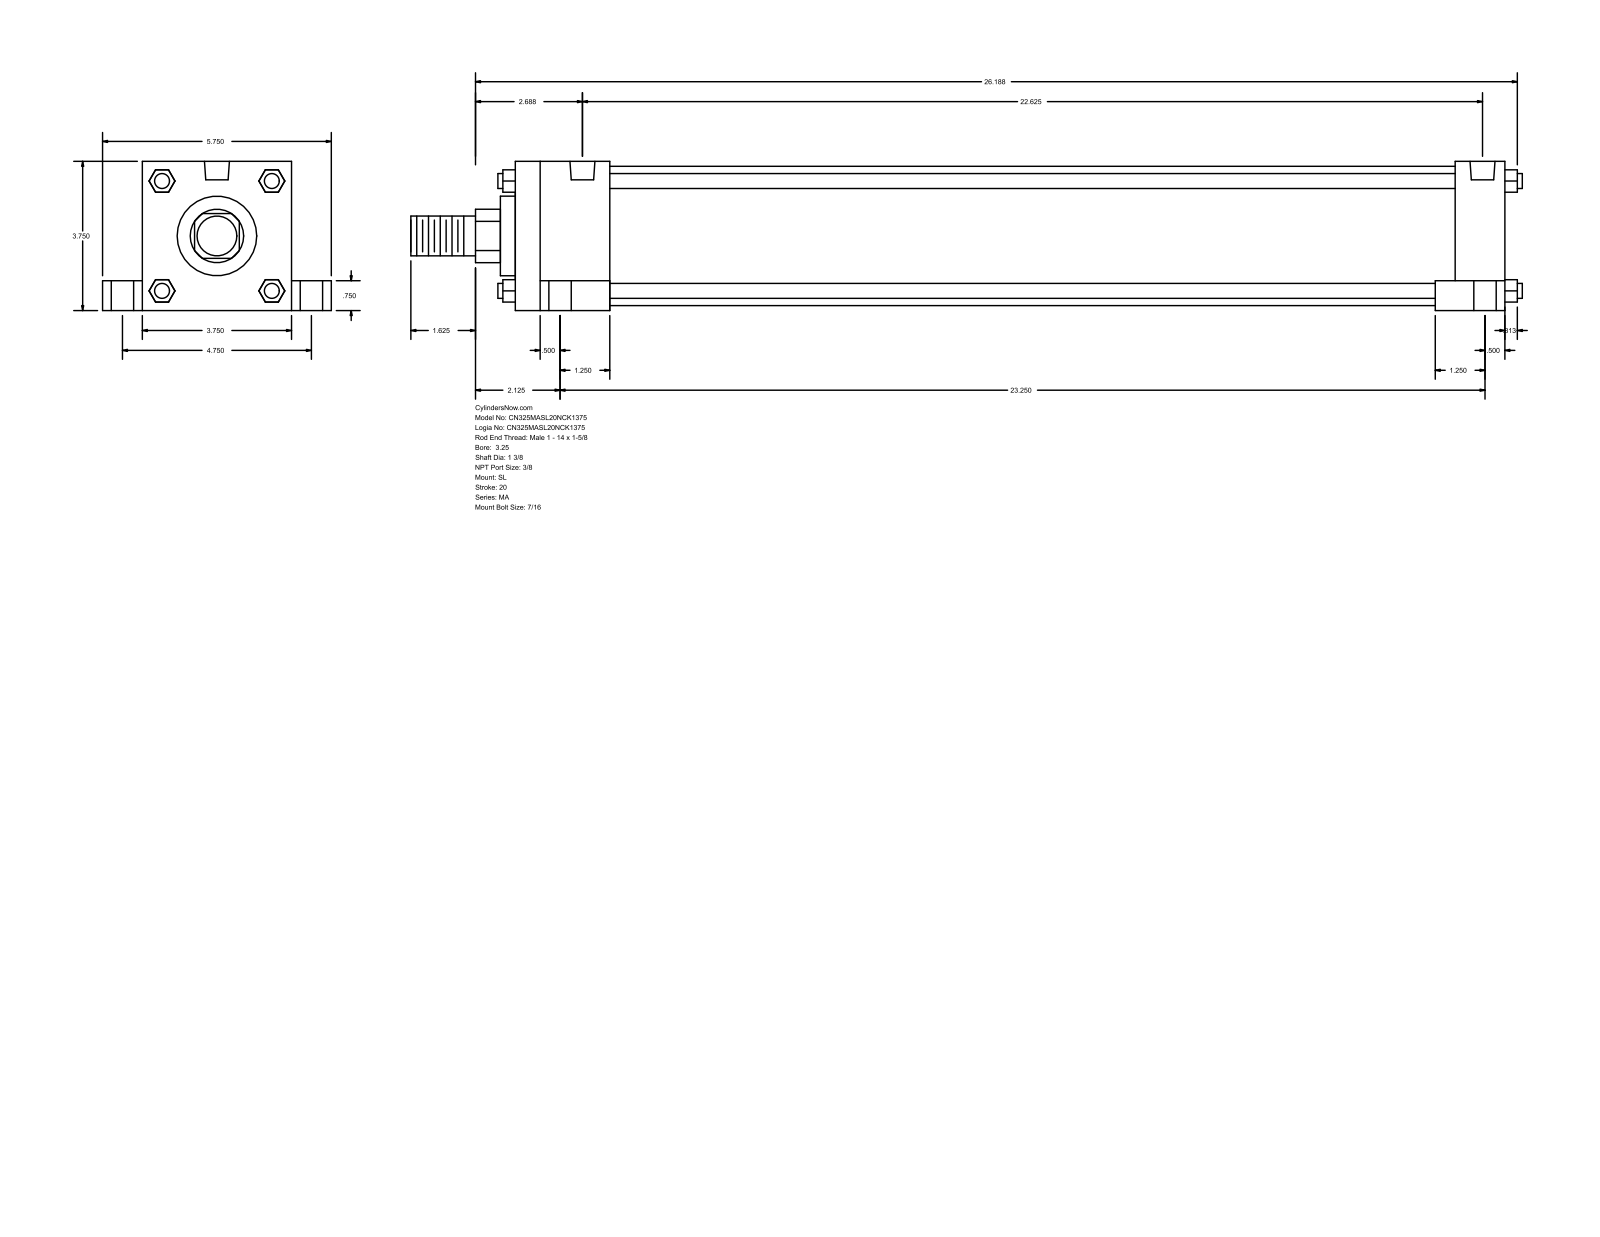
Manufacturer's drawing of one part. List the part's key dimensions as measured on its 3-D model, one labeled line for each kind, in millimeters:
Part name (STEP PRODUCT): MA_SL__0325_1.375
STEP written by: GSSL Pune (CONFIG_CONTROL_DESIGN)
Units: millimetres
Bodies: 0 solids, 148 faces (112 planar, 36 cylindrical, 0 other)
Overall size (bounding box): 709.61 × 146.05 × 95.25
Round holes (diameter × count): ⌀11.11 ×4, ⌀14.29 ×4, ⌀20.64 ×4, ⌀15.93 ×2
Round bosses / shafts (diameter × count): ⌀9.53 ×4, ⌀88.9 ×1, ⌀50.8 ×1, ⌀34.92 ×1, ⌀25.4 ×1
Partial cylindrical surfaces — rounded edges, fillets, slot ends (radius × count): R17.06 ×1
Main face-to-face distances: 95.24, 631.83, 25.41, 120.65, 600.08, 31.75, 60.32, 539.76, 571.51, 19.05
Hole centre spacings: 4.77, 60.35, 60.66, 62, 63.27, 120.66, 565.14, 569.91
